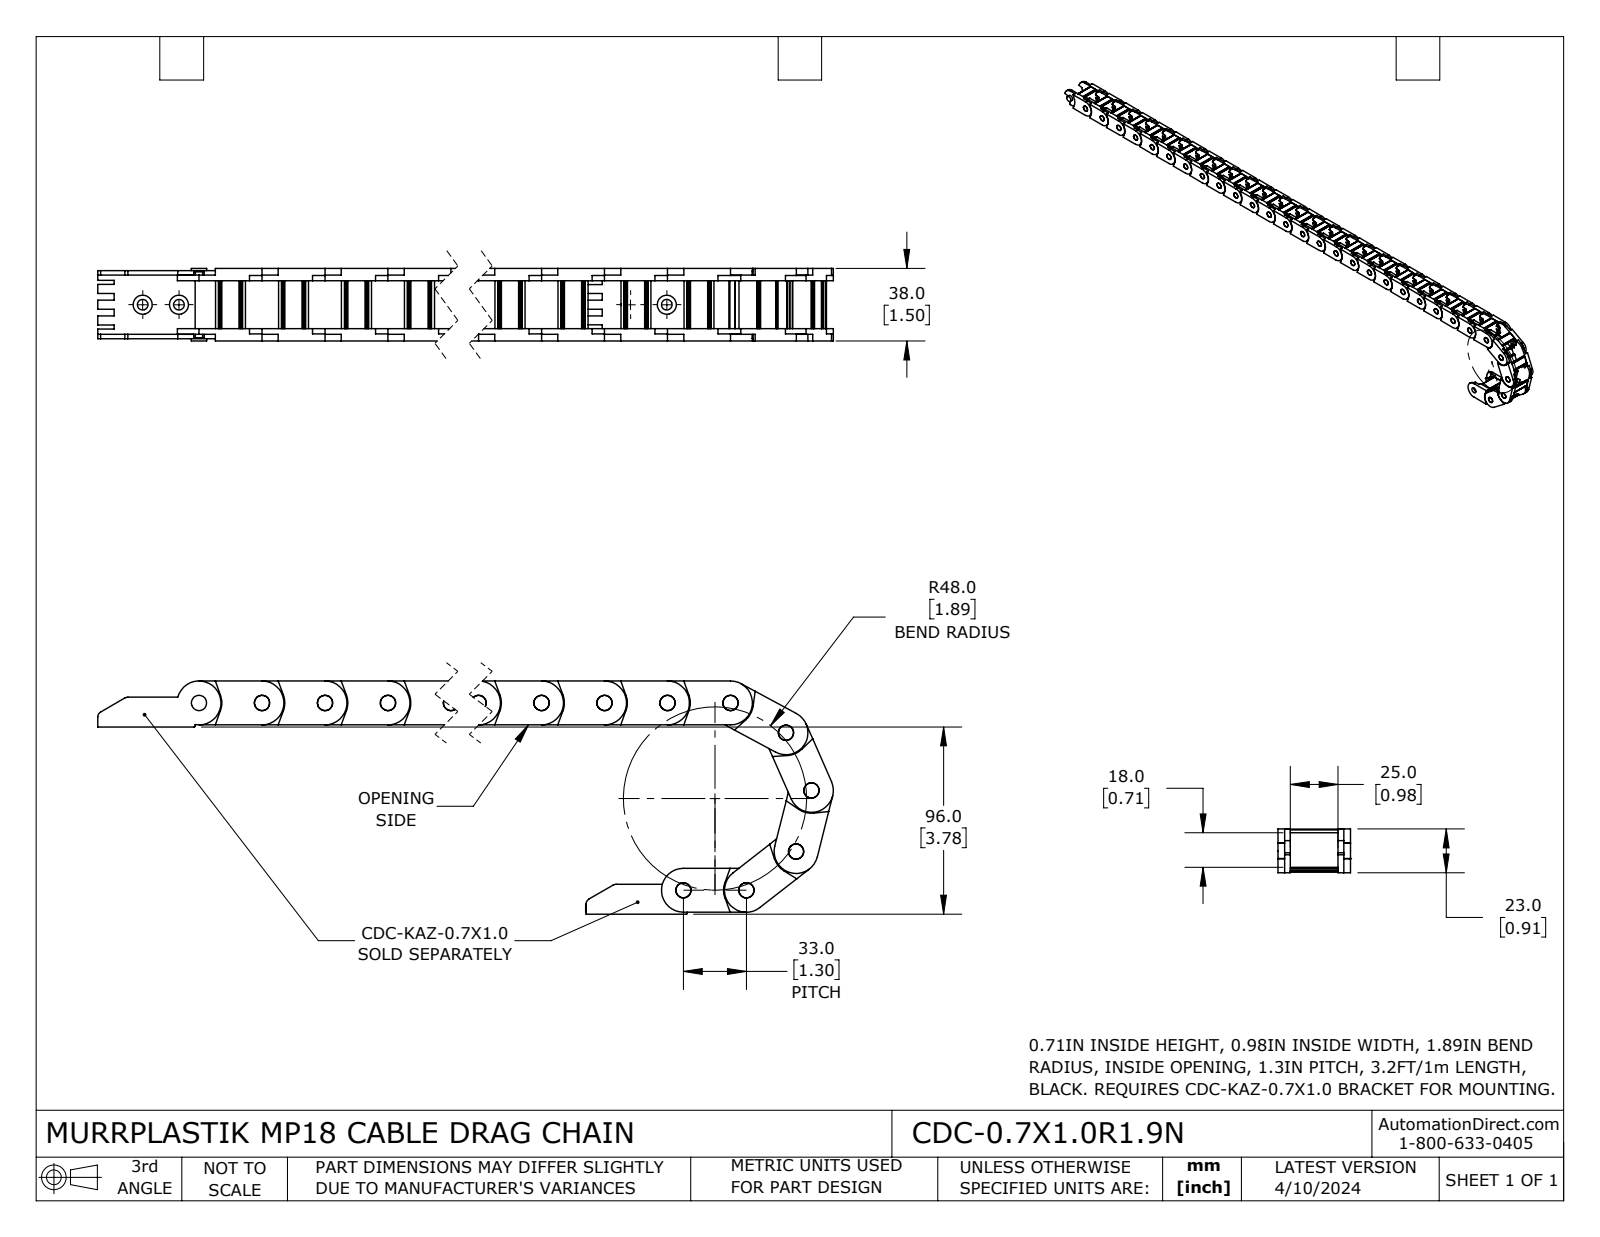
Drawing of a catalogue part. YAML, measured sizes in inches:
part_name: "CDC-0.7X1.0R1.9N"
step_written_by: "SolidWorks 2023 (CONFIG_CONTROL_DESIGN)"
units: inches
bodies: {solids: 30, faces: 2550, planar: 1290, cylindrical: 1260, other: 0}
overall_size: [35.048, 4.767, 1.496]
volume: 18.75
surface_area: 347
round_holes:
  - {diameter: 0.315, count: 30}
round_bosses_or_shafts:
  - {diameter: 0.315, count: 1}
partial_cylinders:
  - {radius: 0.02, count: 120}
  - {radius: 0.059, count: 120}
  - {radius: 0.008, count: 60}
  - {radius: 0.012, count: 60}
  - {radius: 0.453, count: 31}
  - {radius: 0.47, count: 31}
  - {radius: 0.197, count: 30}
  - {radius: 0.215, count: 30}
face_to_face_distances: [0.256, 1.24, 1.496, 0.138, 1.358, 0.118, 1.102, 0.984, 0.146, 1.35]
hole_center_spacings: [1.299, 2.598, 3.898, 5.197, 6.496, 7.795, 9.094, 10.394]
